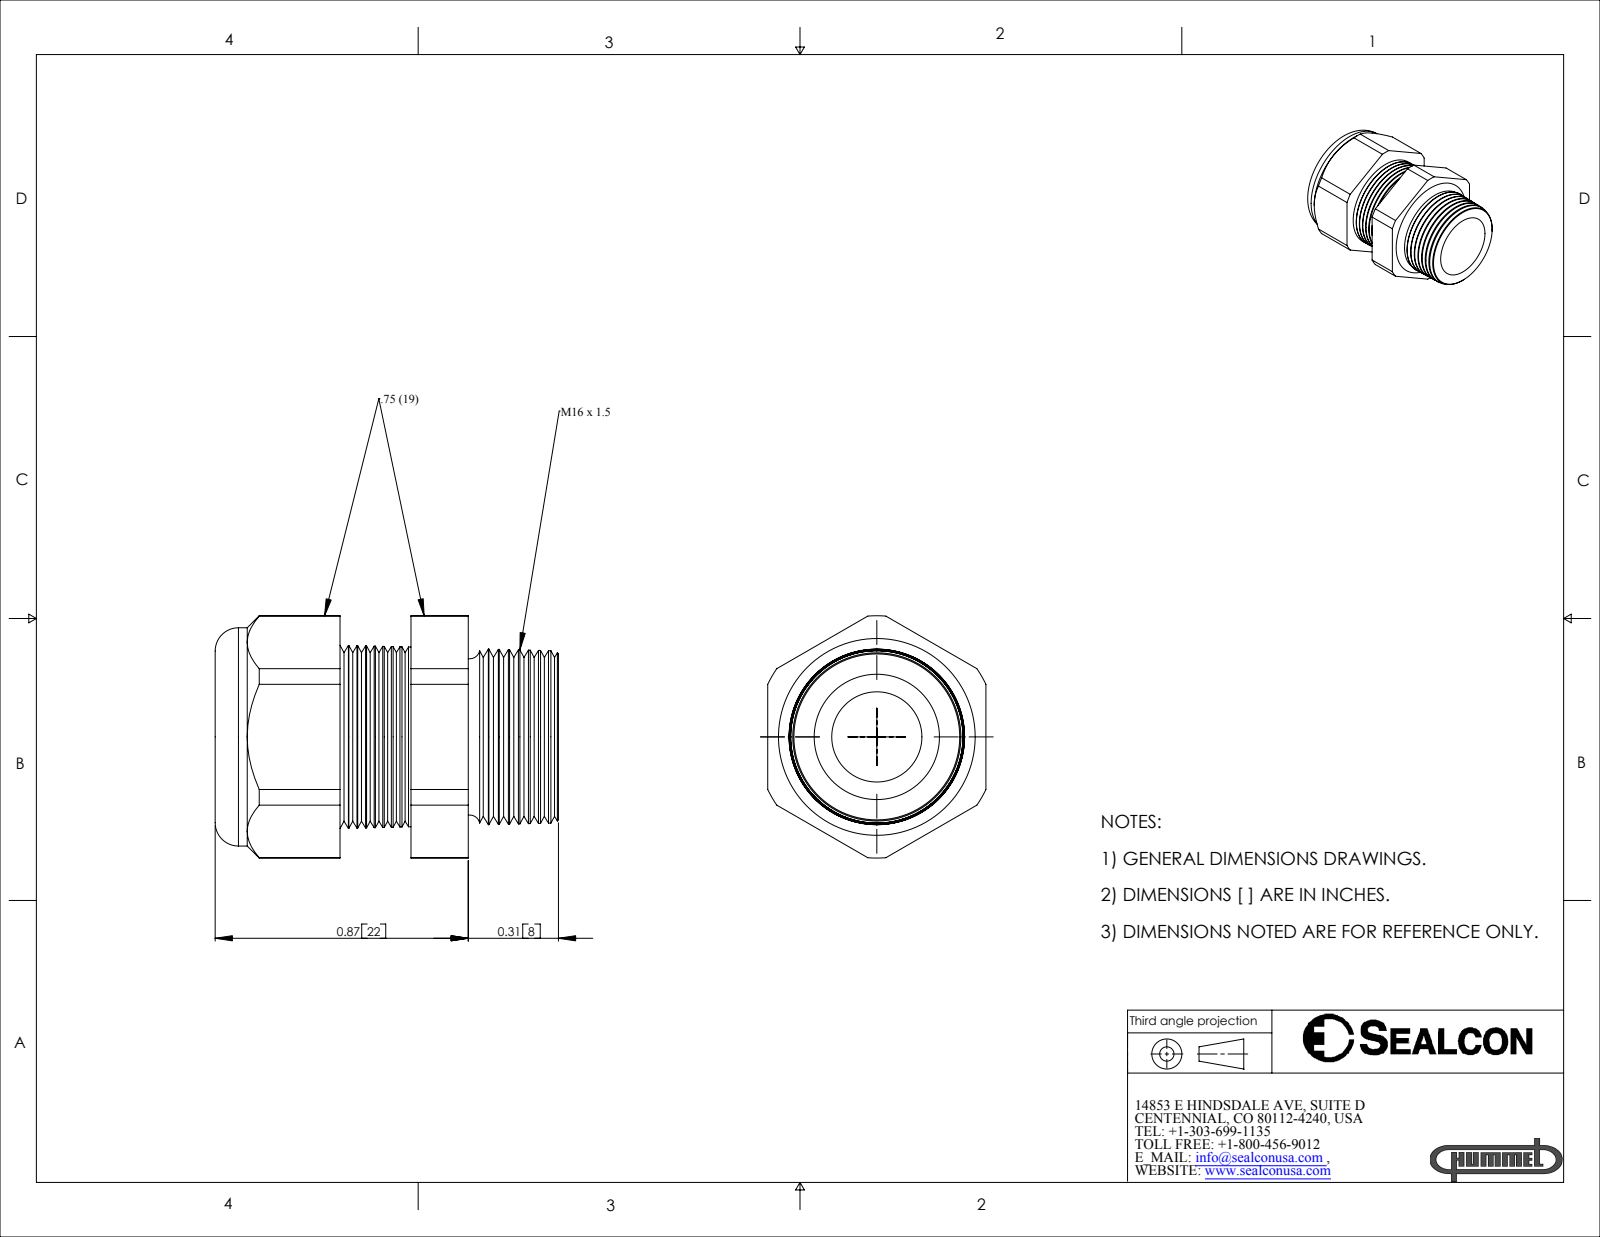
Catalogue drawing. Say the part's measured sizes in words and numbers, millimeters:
The part is named "CD16MP-GY". Its 3-D file was written by "SolidWorks 2007 (CONFIG_CONTROL_DESIGN)". It is 2 solids with 150 faces: 20 planar, 20 cylindrical and 110 other. Overall it measures 30 by 21.2 by 19.1 millimeters. Its volume is 5 520 cubic millimeters and its surface area 3 942 square millimeters. Round holes: 1 of diameter 7.4, 1 of diameter 7.9. Round bosses or shafts: 1 of diameter 19.1. Partial cylindrical surfaces (rounded edges, fillets, slot ends): 1 of radius 10.6. The main face-to-face distances are 19.1, 17.1, 19.1, 10.9, 6.2, 22.1, 11.2, 5, 30, 19.1.
